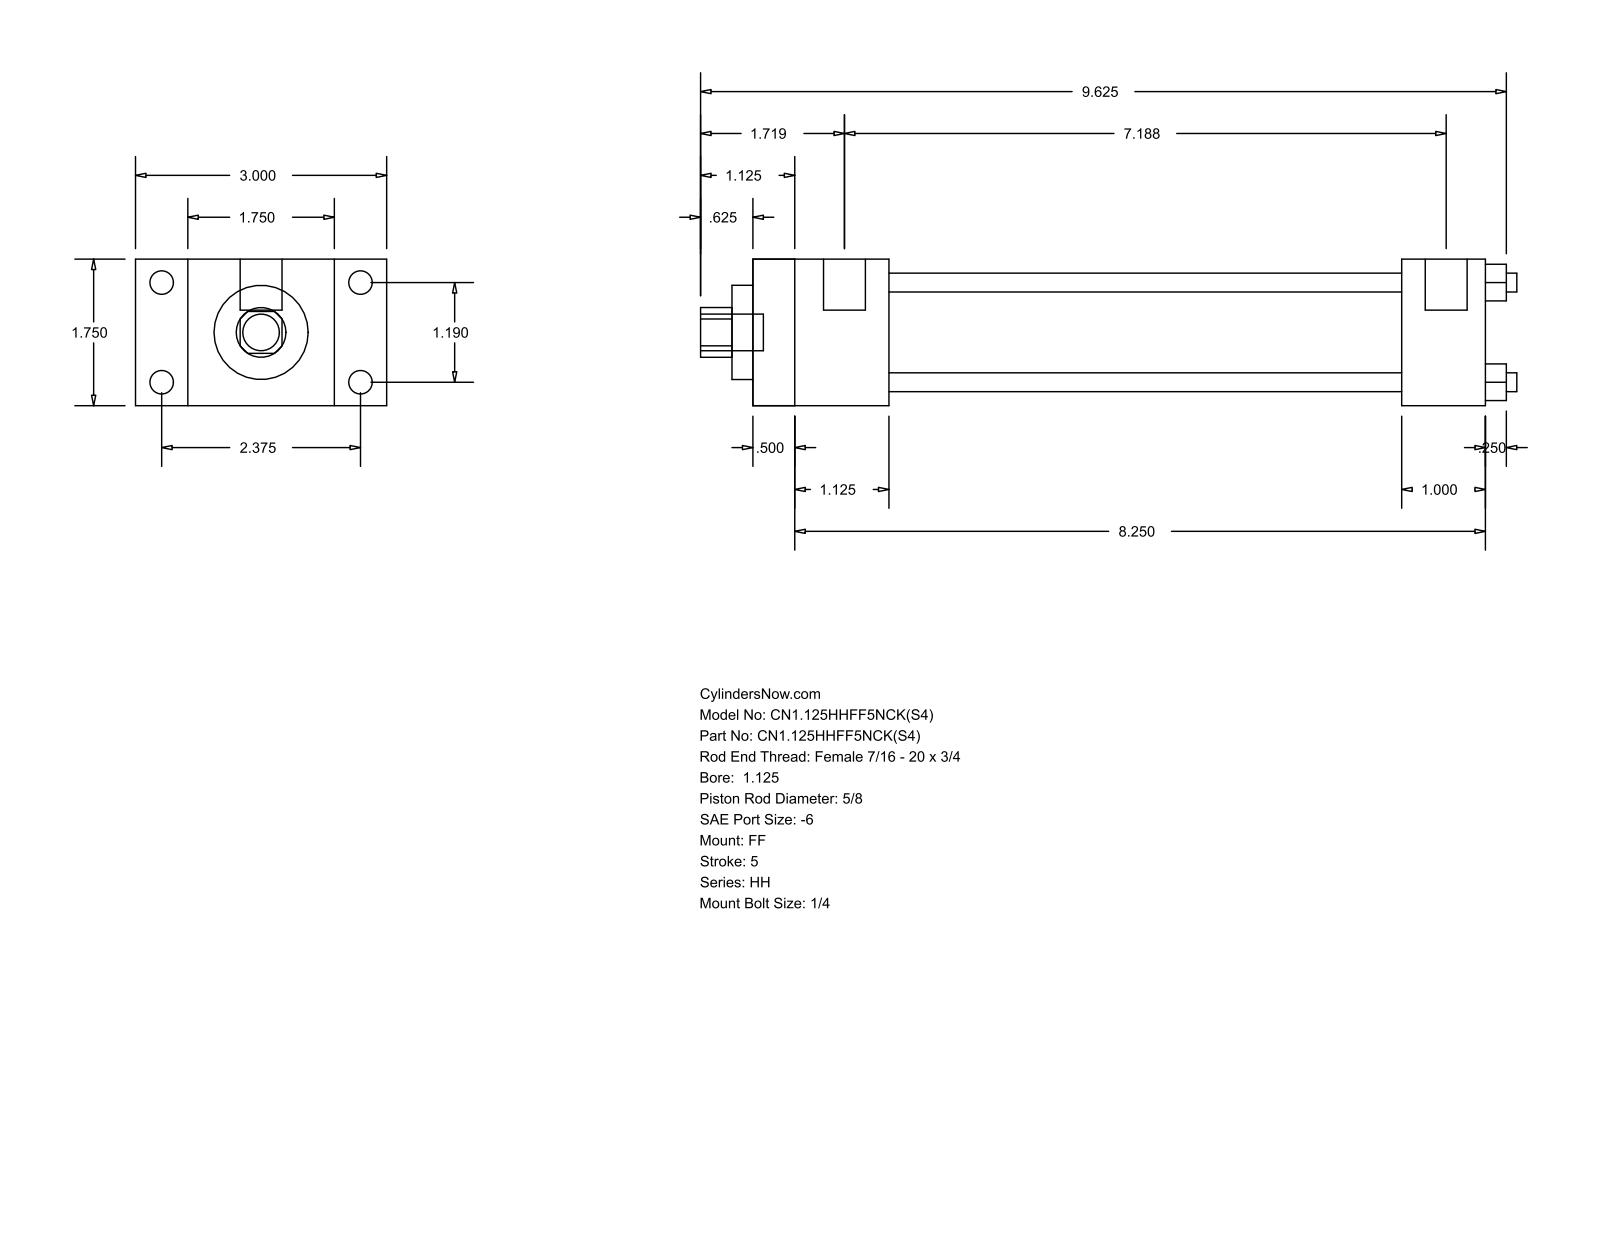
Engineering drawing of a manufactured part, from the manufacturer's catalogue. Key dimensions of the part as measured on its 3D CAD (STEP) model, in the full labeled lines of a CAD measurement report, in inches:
Part name (STEP PRODUCT): HH_FF__0112_0.625
STEP written by: GSSL Pune (CONFIG_CONTROL_DESIGN)
Units: inches
Bodies: 0 solids, 92 faces (64 planar, 28 cylindrical, 0 other)
Overall size (bounding box): 9.75 × 3 × 1.75
Round holes (diameter × count): ⌀0.225 ×4, ⌀0.625 ×1, ⌀1.125 ×1, ⌀1.375 ×1
Round bosses / shafts (diameter × count): ⌀0.281 ×4, ⌀0.219 ×4, ⌀0.5 ×2, ⌀0.437 ×1
Partial cylindrical surfaces — rounded edges, fillets, slot ends (radius × count): R0.297 ×1
Main face-to-face distances: 1.75, 8.75, 0.625, 0.5, 8.25, 2.375, 1.125, 1.625, 7.75, 7.25
Hole centre spacings: 0.841, 1.19, 1.683
